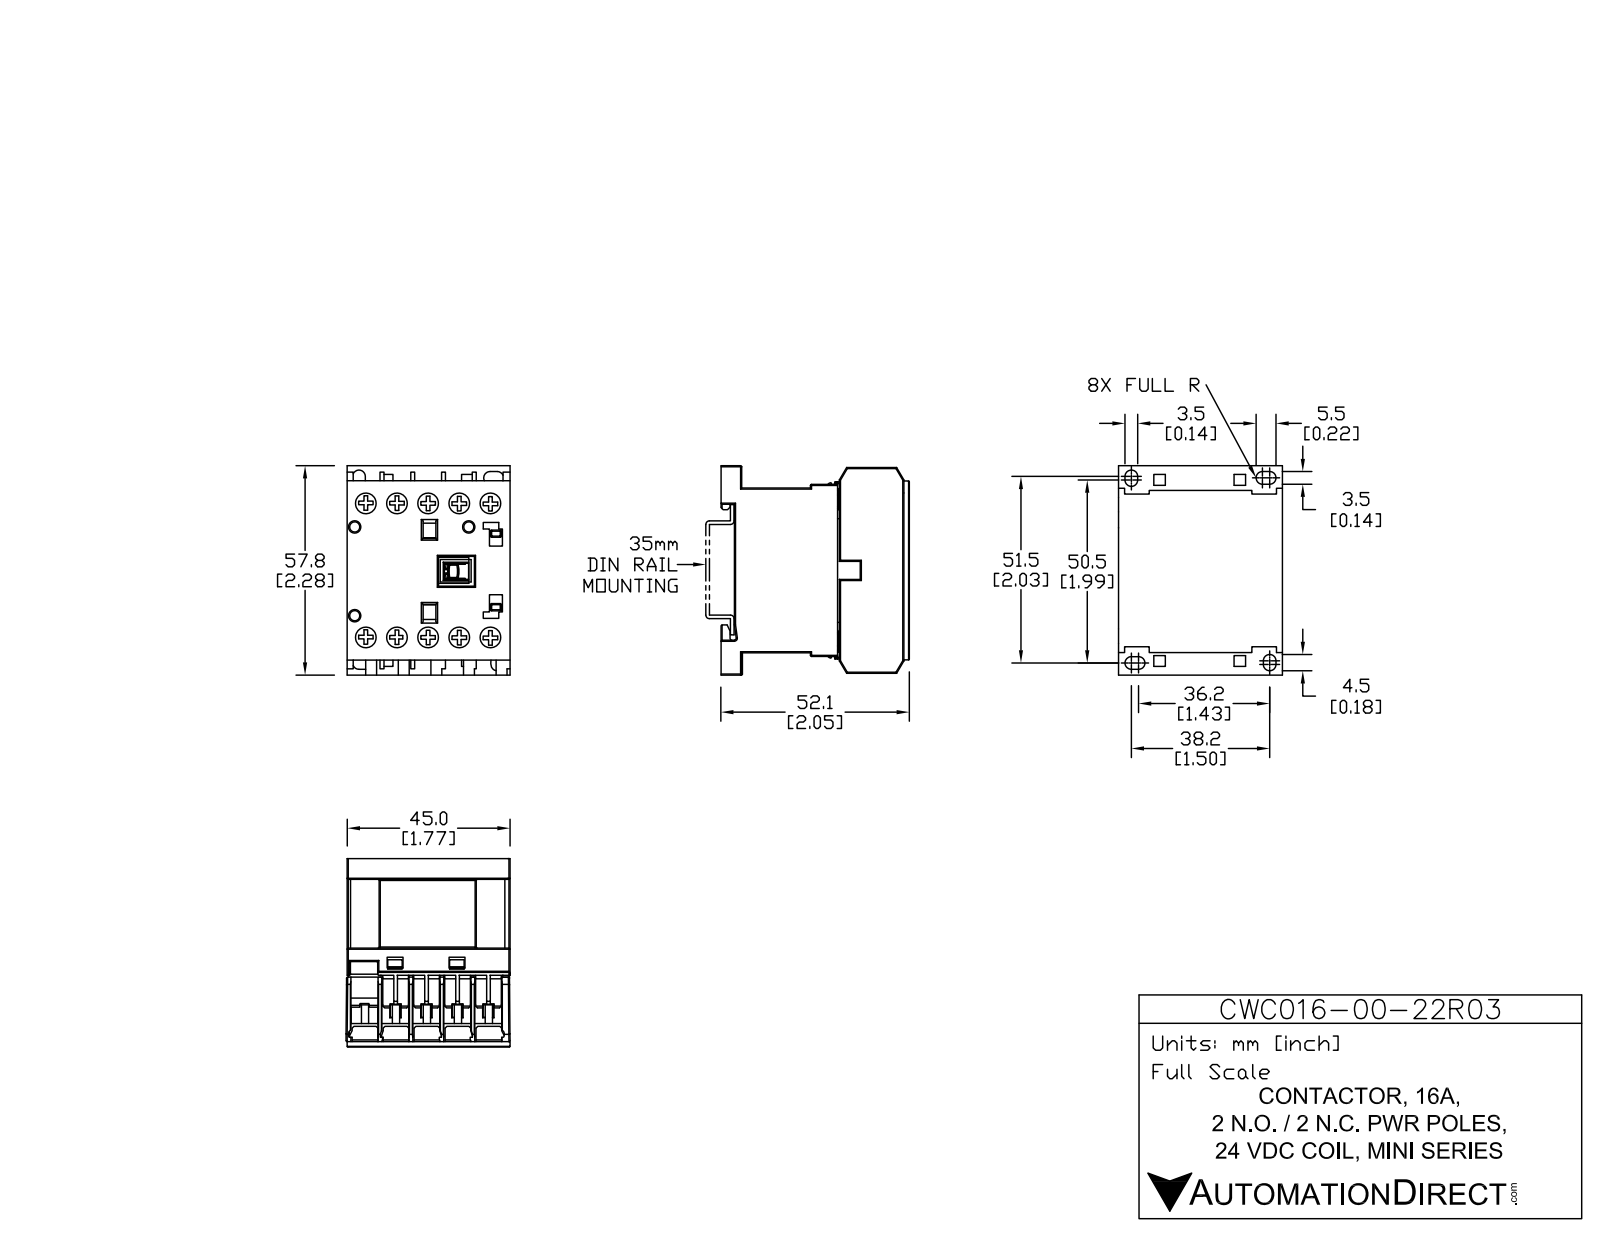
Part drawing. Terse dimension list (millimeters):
name: CWC16-00-22R03
written by: SolidWorks 2013 (AUTOMOTIVE_DESIGN)
unit: mm
bodies: 15 solids, 535 faces (445 planar, 90 cylindrical, 0 other)
size: 58.04 × 52.12 × 45.75
volume: 97 133 mm³; area: 30 437 mm²
holes: 10× ⌀6.2, 3× ⌀2.8
bosses: 10× ⌀5.9
rounds: 20× R0.3, 6× R1.72, 2× R1.73, 1× R0.32, 1× R0.42, 1× R0.55
face distances: 8.25, 45.5, 1.25, 16.5, 9.5, 5.5, 17.75, 5.13, 10.63, 7
hole spacings: 8.55, 37.94, 17.1, 40.72, 36.96, 25.65, 44.99, 6.91
